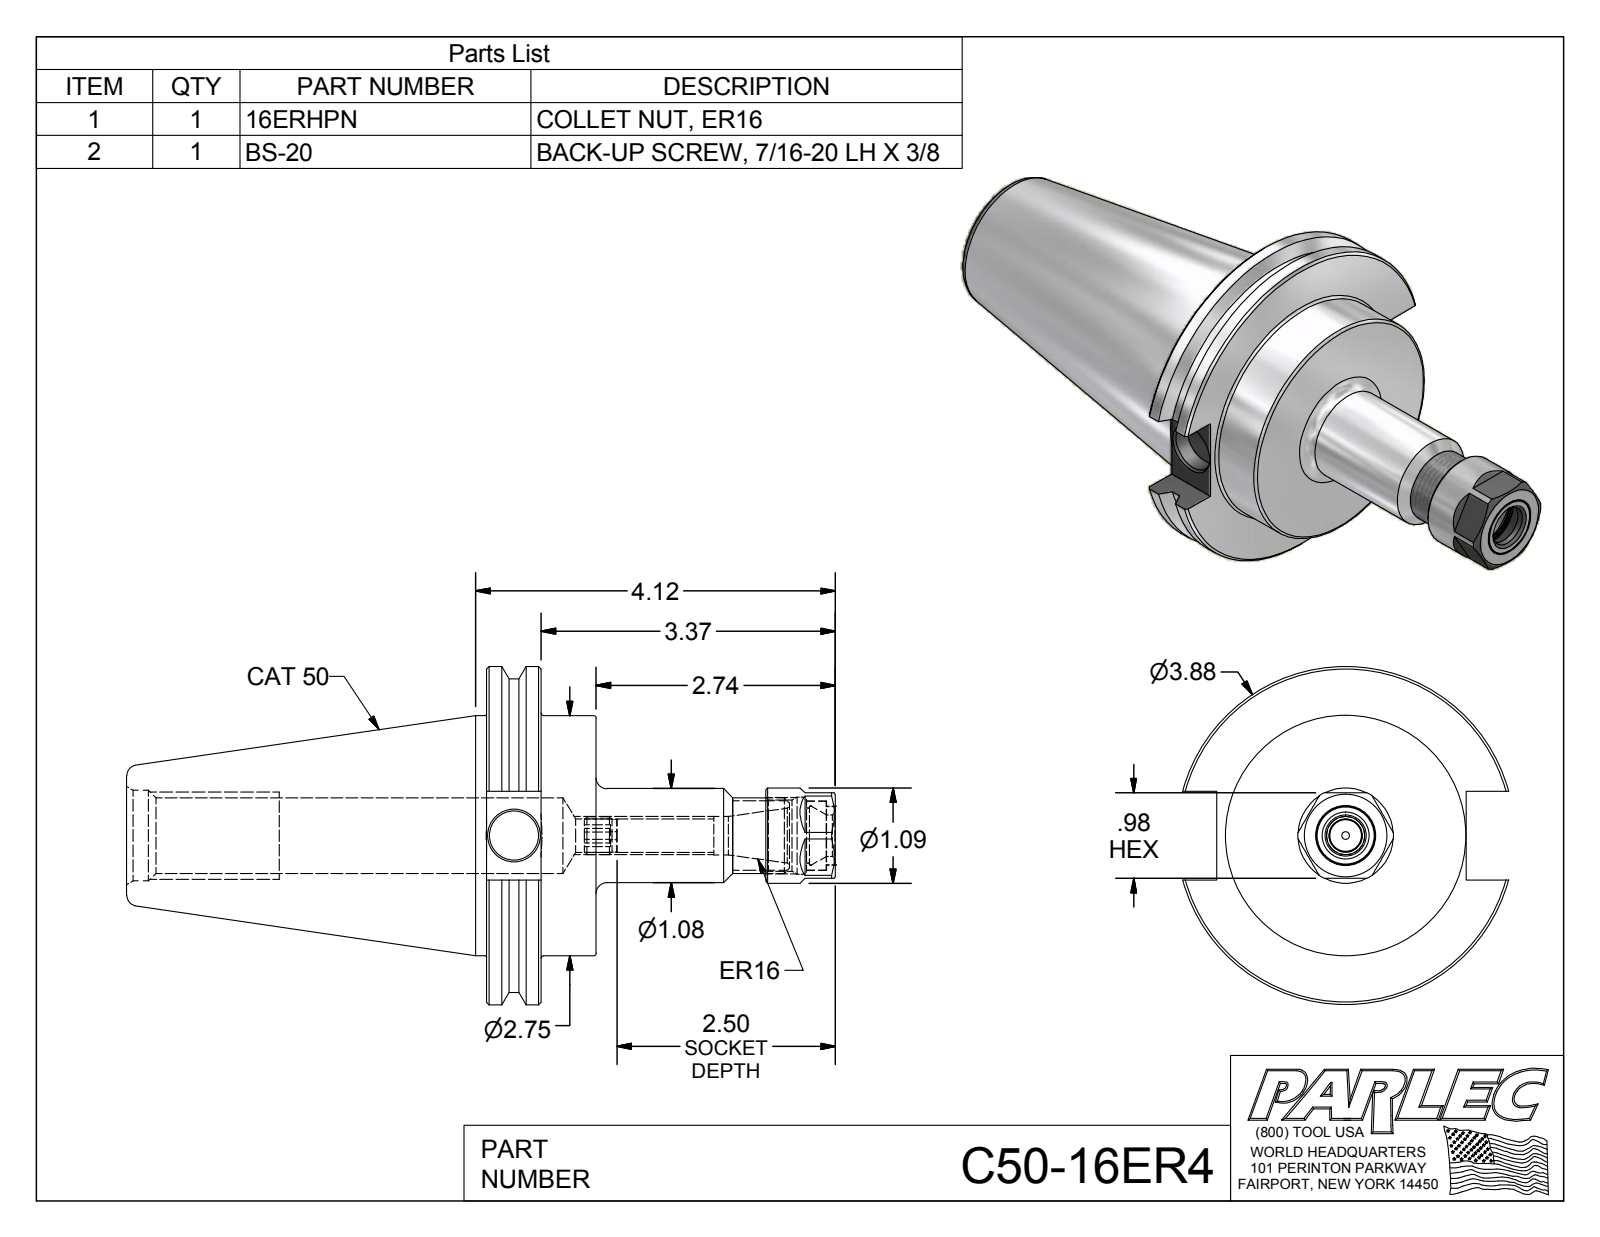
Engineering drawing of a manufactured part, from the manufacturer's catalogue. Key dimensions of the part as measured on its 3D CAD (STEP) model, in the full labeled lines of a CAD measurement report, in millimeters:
Part name (STEP PRODUCT): C50-16ER4; C50-16ER4-1; 16ERHPN; BS-20
STEP written by: Autodesk Inventor 2012 (AUTOMOTIVE_DESIGN)
Units: millimetres
Bodies: 4 solids, 108 faces (41 planar, 28 cylindrical, 39 other)
Overall size (bounding box): 206.2 × 98.4 × 95
Volume: 405 900 mm³ · Surface area: 59 900 mm²
Round holes (diameter × count): ⌀2.3 ×1, ⌀9.7 ×1, ⌀11.2 ×1, ⌀12 ×1, ⌀14.3 ×1, ⌀16 ×1, ⌀17.1 ×1, ⌀17.3 ×1, ⌀20.2 ×1, ⌀20.7 ×1, ⌀22 ×1, ⌀22.4 ×1
Round bosses / shafts (diameter × count): ⌀98.4 ×1, ⌀91.3 ×1, ⌀69.9 ×1, ⌀27.7 ×1, ⌀27.4 ×1, ⌀22 ×1, ⌀20.1 ×1, ⌀17 ×1
Main face-to-face distances: 15.9, 31.9, 16, 104.8, 120.7, 136.7, 25.8, 24.9, 206.2, 101.5
